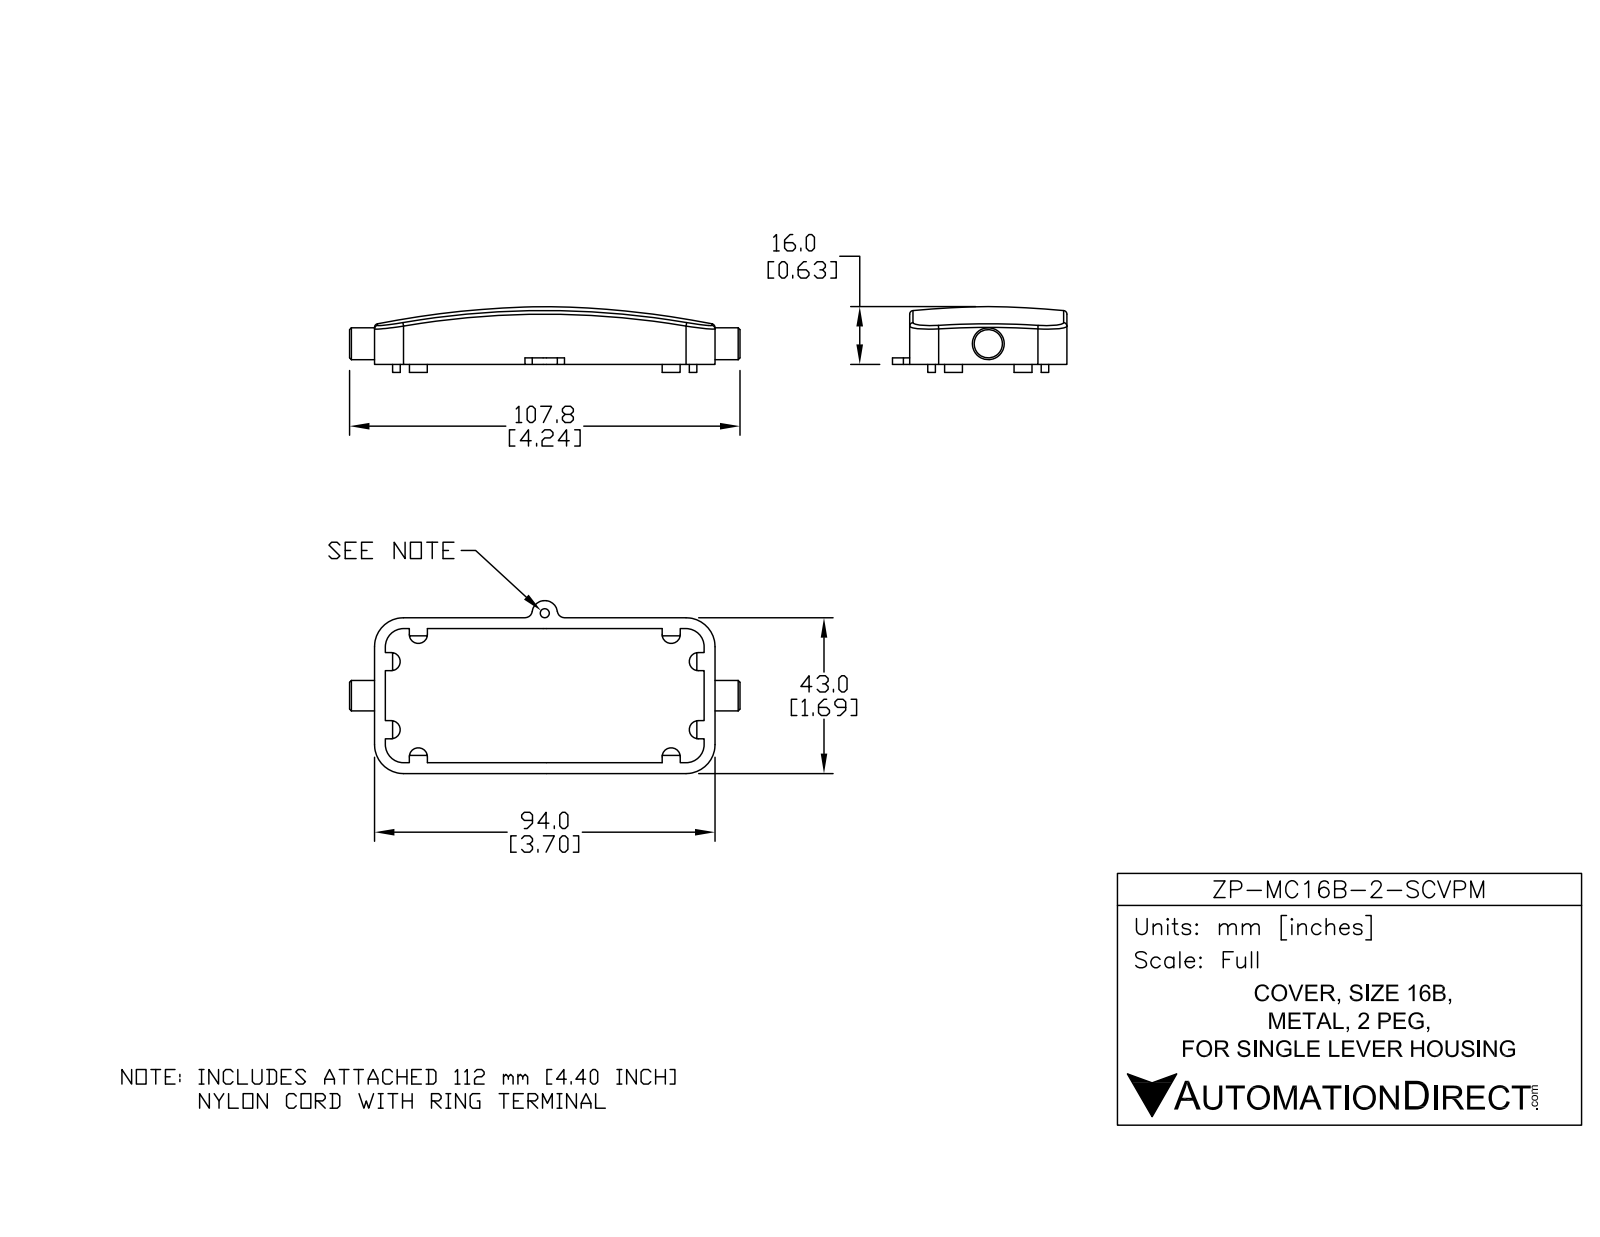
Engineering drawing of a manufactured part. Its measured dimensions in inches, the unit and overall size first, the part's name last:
Units: inches
Overall size (bounding box): 5.765 × 4.22 × 2.573
Round holes (diameter × count): ⌀0.098 ×1, ⌀0.161 ×1
Round bosses / shafts (diameter × count): ⌀0.346 ×1
Partial cylindrical surfaces — rounded edges, fillets, slot ends (radius × count): R0.098 ×8, R0.018 ×4, R0.197 ×4, R0.315 ×4, R0.024 ×2, R0.079 ×2, R0.236 ×2, R0.138 ×1
Main face-to-face distances: 0.118, 1.591, 1.709, 1.472, 3.559, 3.677, 0.378, 0.197, 3.441, 0.575
Volume: 1.353 in³ · Surface area: 24.72 in²
Bodies: 4 solids, 129 faces (71 planar, 38 cylindrical, 20 other)
Part name (STEP PRODUCT): ZP-MC16B-2-SCVPM
STEP written by: SolidWorks 2014 (AUTOMOTIVE_DESIGN)
